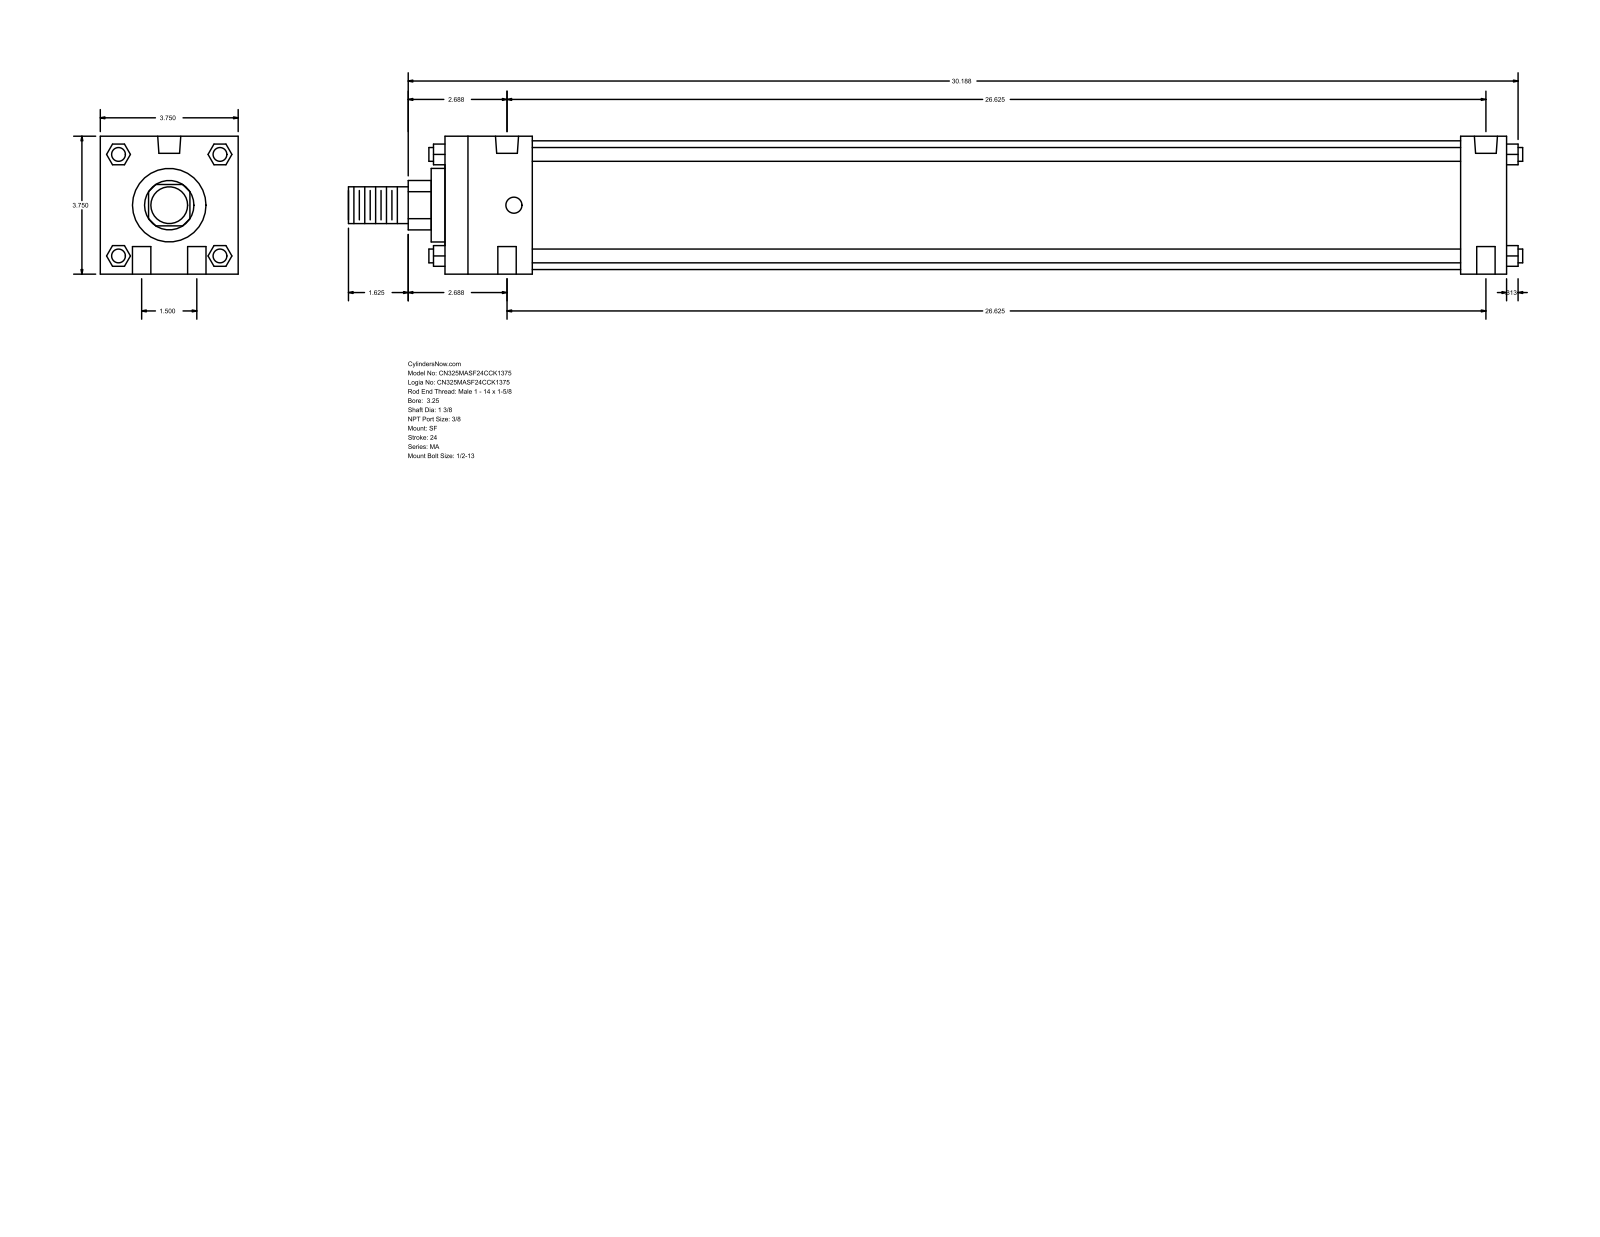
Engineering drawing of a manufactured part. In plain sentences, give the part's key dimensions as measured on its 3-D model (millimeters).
The part is named "MA_SF__0325_1.375". Its 3-D file was written by "GSSL Pune (CONFIG_CONTROL_DESIGN)". It is 0 solids with 124 faces: 94 planar, 30 cylindrical and 0 other. Overall it measures 811.21 by 95.25 by 95.25 millimeters. Round holes: 4 of diameter 12.7, 2 of diameter 11.11, 2 of diameter 15.93. Round bosses or shafts: 4 of diameter 9.53, 1 of diameter 88.9, 1 of diameter 50.8, 1 of diameter 34.92, 1 of diameter 25.4. Partial cylindrical surfaces (rounded edges, fillets, slot ends): 1 of radius 17.06. The main face-to-face distances are 95.24, 733.43, 701.68, 31.75, 60.32, 641.36, 673.11, 9.52, 69.84, 711.2. The hole center spacings are 19.05, 676.55, 676.28, 38.1, 677.35, 666.74.
